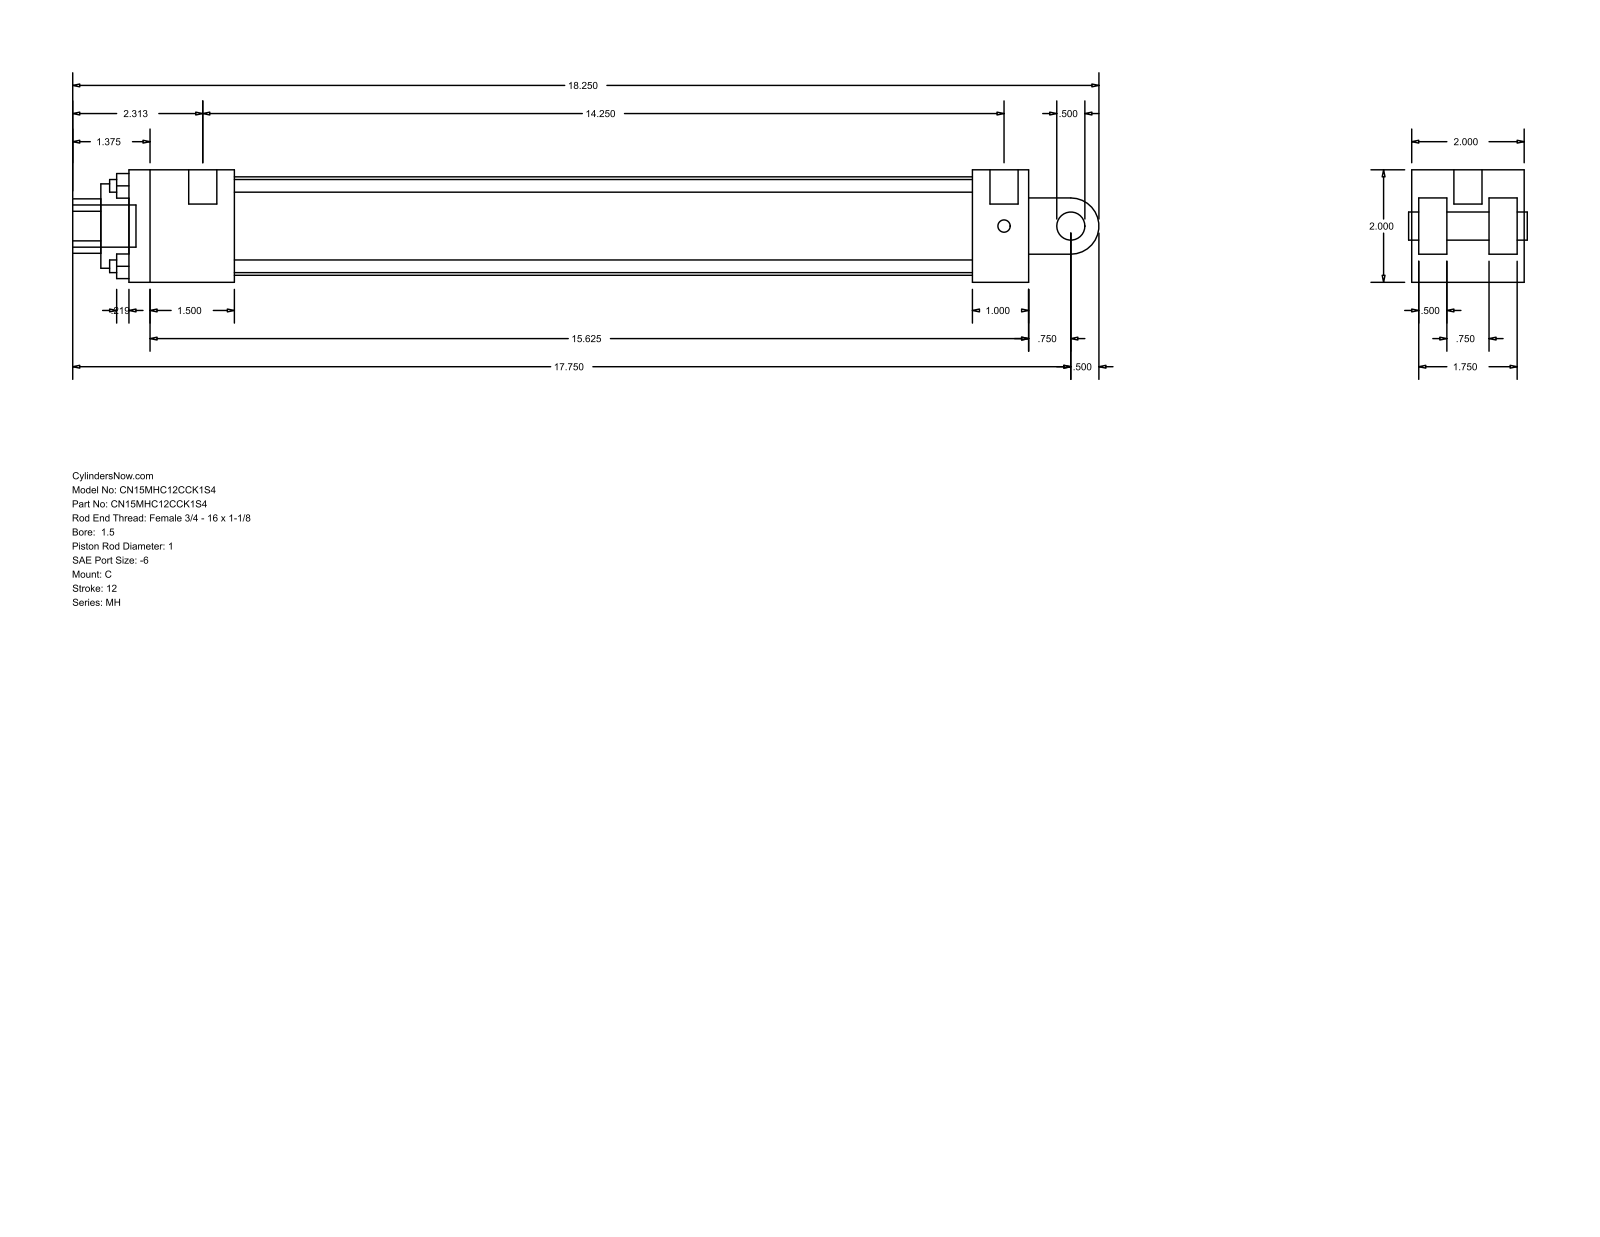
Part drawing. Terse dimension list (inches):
name: MH_C__0150_1
written by: GSSL Pune (CONFIG_CONTROL_DESIGN)
unit: in
bodies: 0 solids, 99 faces (70 planar, 29 cylindrical, 0 other)
size: 18.25 × 2 × 2
holes: 4× ⌀0.225, 2× ⌀0.219, 1× ⌀0.5, 1× ⌀1, 1× ⌀1.5, 1× ⌀1.75
bosses: 2× ⌀0.5, 2× ⌀0.219, 1× ⌀0.75
rounds: 1× R0.484, 1× R0.5
face distances: 2, 0.5, 1.875, 0.125, 0.625, 1, 1.375, 1.25, 16, 1.5
hole spacings: 1.011, 1.43, 2.022
